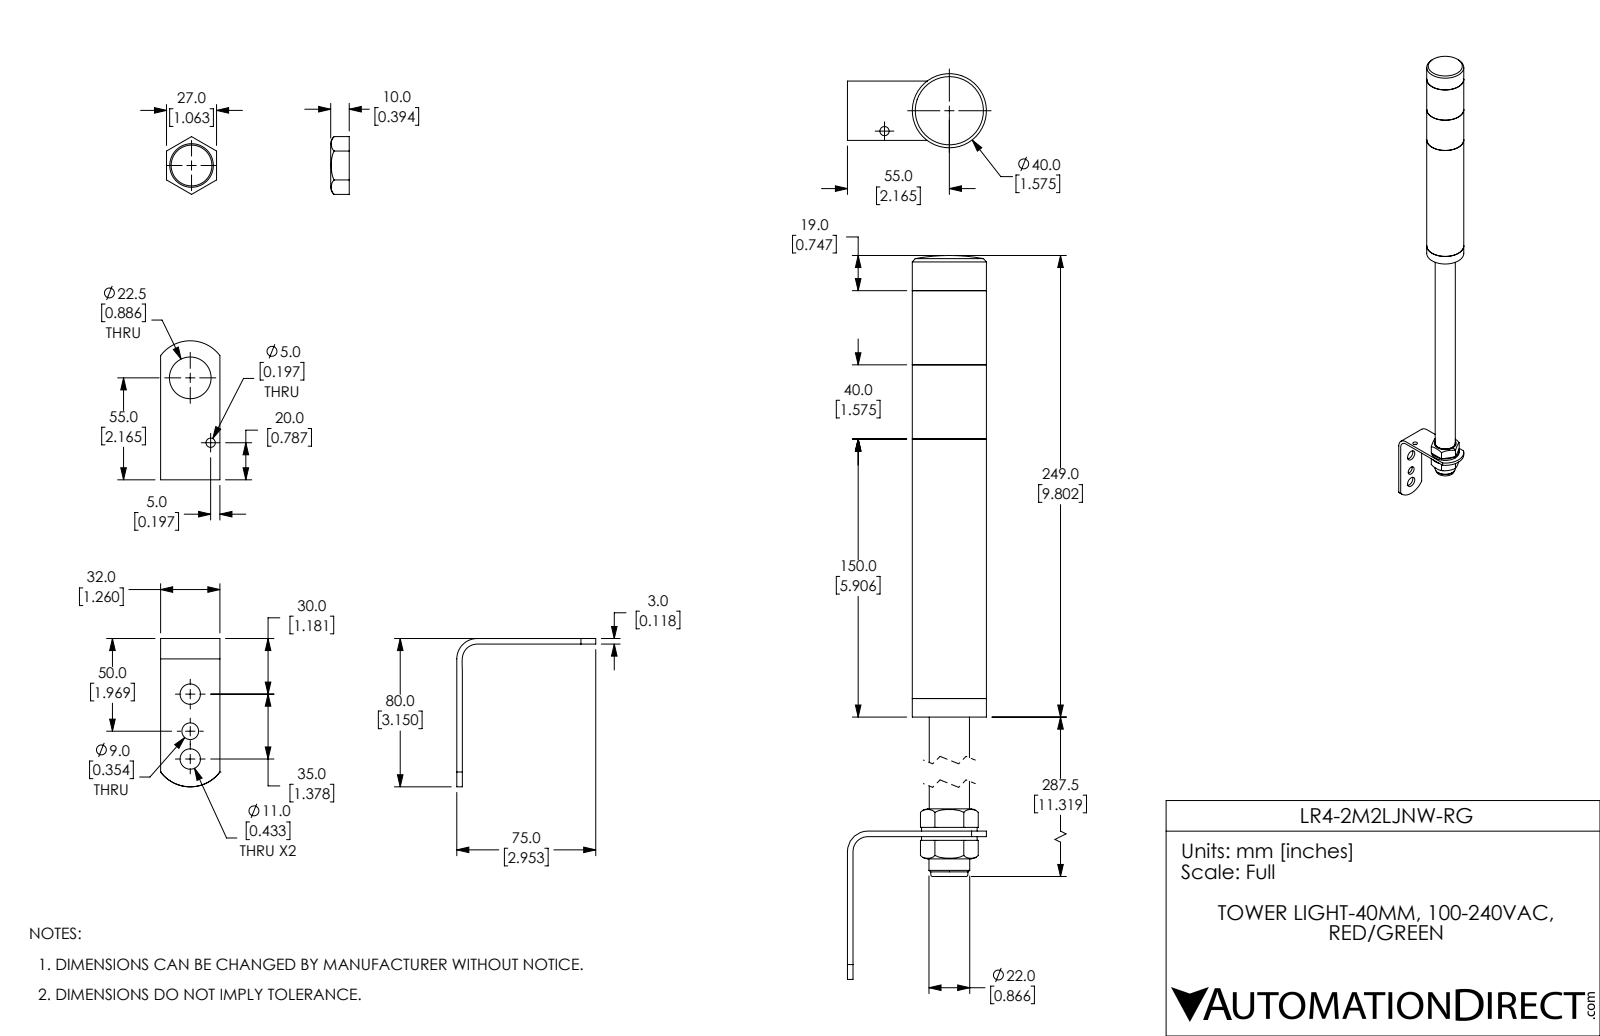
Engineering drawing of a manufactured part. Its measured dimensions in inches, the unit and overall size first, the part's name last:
Units: inches
Overall size (bounding box): 23.306 × 2.953 × 1.575
Round holes (diameter × count): ⌀0.126 ×2, ⌀0.433 ×2, ⌀0.197 ×1, ⌀0.303 ×1, ⌀0.354 ×1, ⌀0.697 ×1, ⌀0.866 ×1, ⌀0.886 ×1, ⌀1.087 ×1, ⌀1.366 ×1, ⌀1.386 ×1, ⌀1.39 ×1
Round bosses / shafts (diameter × count): ⌀1.575 ×1, ⌀1.181 ×1, ⌀0.854 ×1
Partial cylindrical surfaces — rounded edges, fillets, slot ends (radius × count): R0.787 ×1
Main face-to-face distances: 1.575, 3.15, 5.354, 6.929, 8.504, 0.197, 0.406, 10.945, 0.957, 6.311
Hole centre spacings: 0.283, 0.567, 0.591, 0.787, 1.177, 1.378, 1.444, 1.717
Volume: 23.05 in³ · Surface area: 172.1 in²
Bodies: 11 solids, 147 faces (52 planar, 79 cylindrical, 16 other)
Part name (STEP PRODUCT): LR4-2M2LJNW-RG
STEP written by: SolidWorks 2017 (AUTOMOTIVE_DESIGN)
